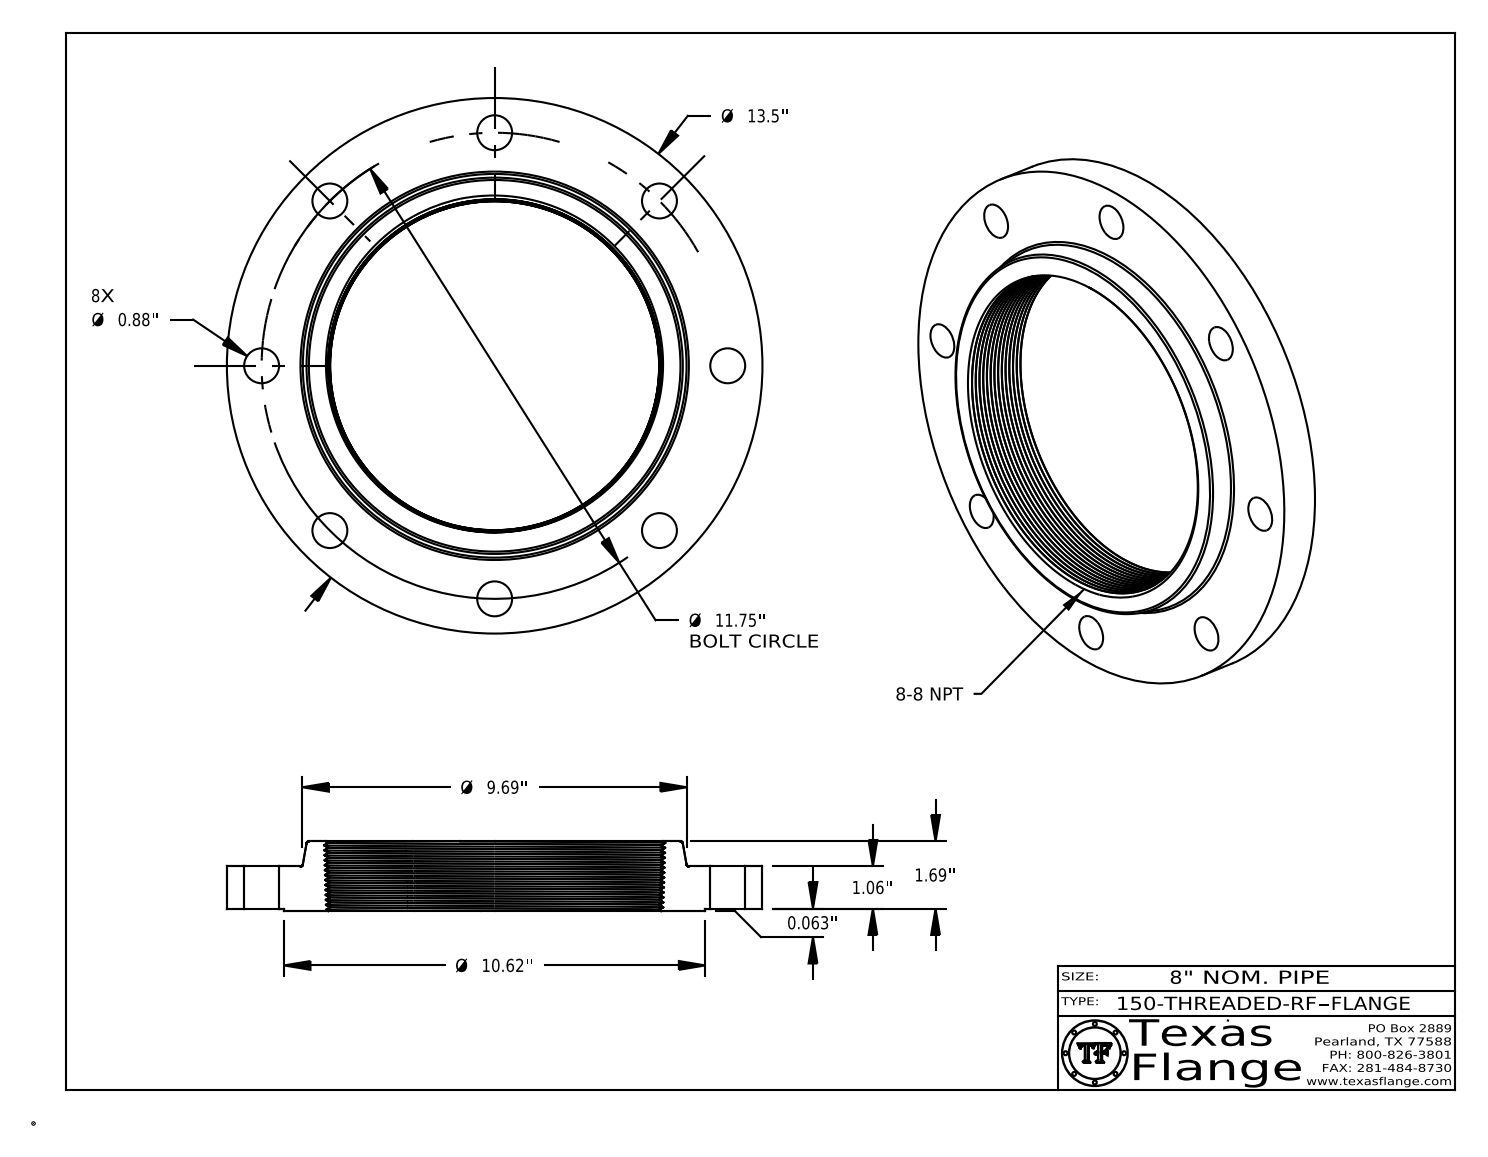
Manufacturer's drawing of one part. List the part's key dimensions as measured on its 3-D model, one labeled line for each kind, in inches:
Part name (STEP PRODUCT): 150-THREADED-RF
STEP written by: CATIA V5 STEP AP214 (AUTOMOTIVE_DESIGN)
Units: inches
Bodies: 1 solid, 563 faces (369 planar, 40 cylindrical, 154 other)
Overall size (bounding box): 13.5 × 13.5 × 1.753
Volume: 99.42 in³ · Surface area: 337.3 in²
Round holes (diameter × count): ⌀0.88 ×8, ⌀0.495 ×1
Round bosses / shafts (diameter × count): ⌀0.03 ×8, ⌀13.5 ×1, ⌀10.62 ×1, ⌀0.39 ×1
Main face-to-face distances: 1.06, 0.063, 1.122, 1.753, 1.69, 0.63, 1.107, 1.045, 0.015, 0.645
Hole centre spacings: 4.496, 8.309, 10.856, 11.75, 9.77, 2.292, 2.293, 6.528
